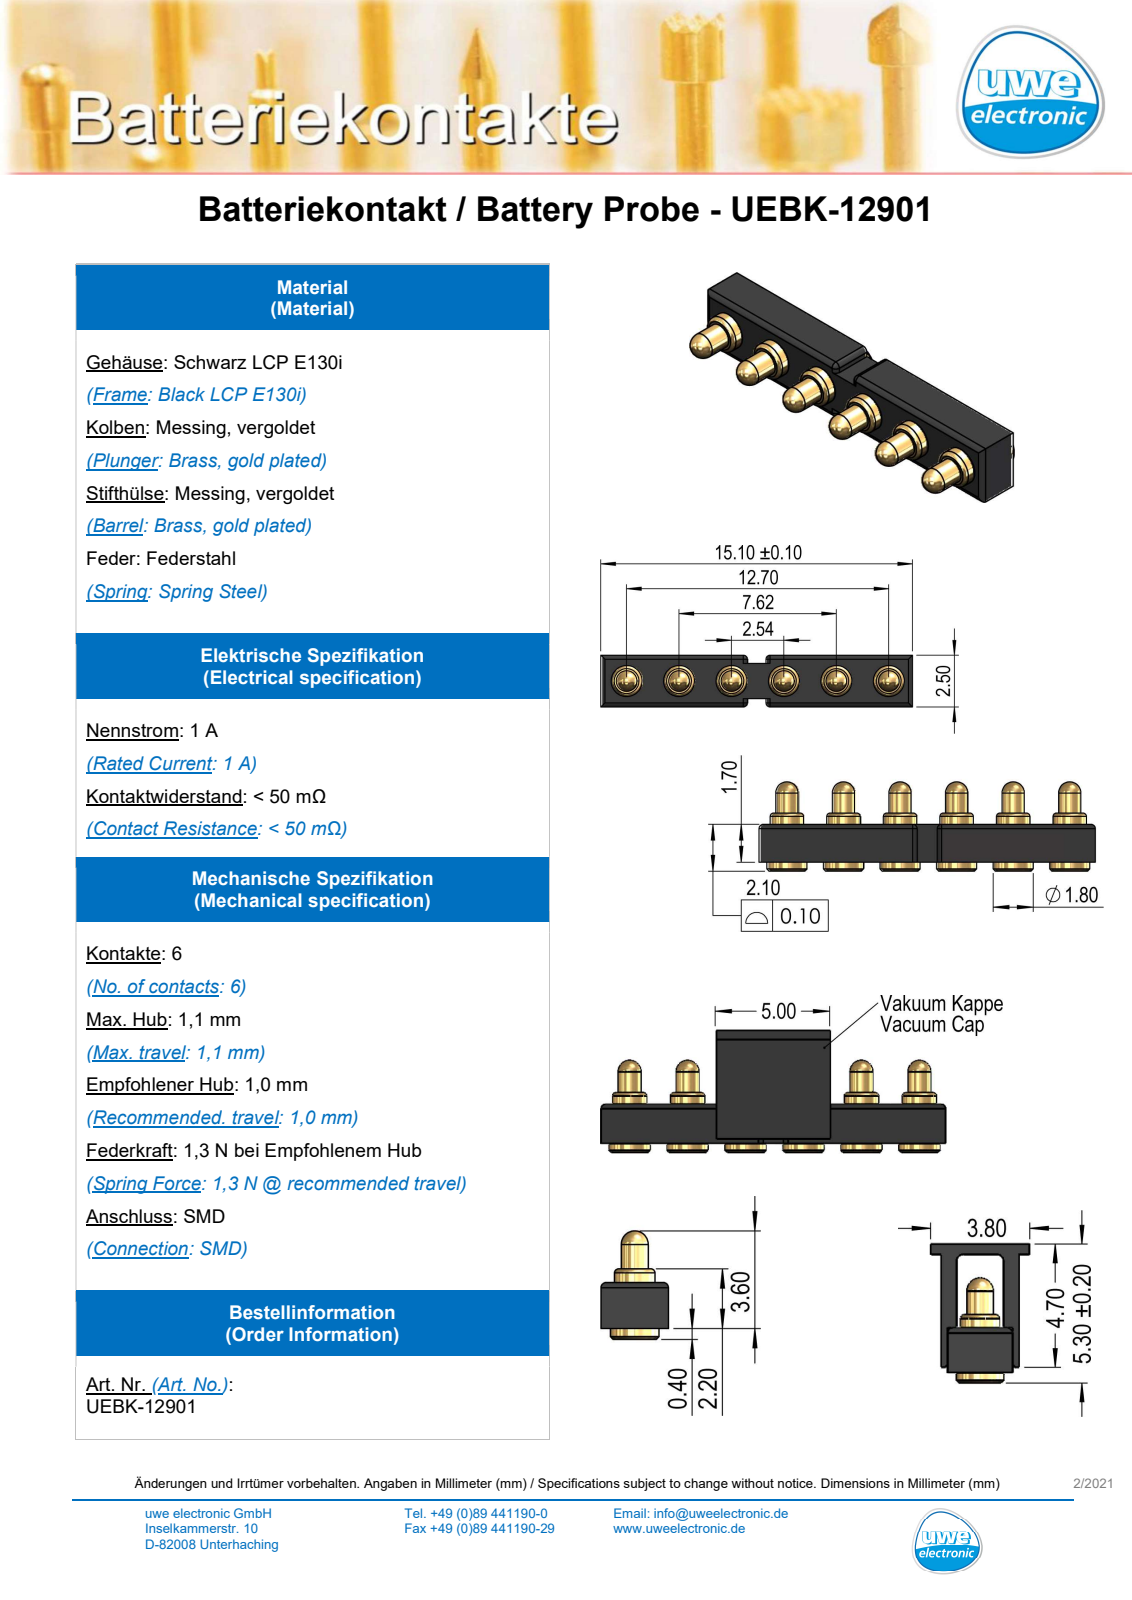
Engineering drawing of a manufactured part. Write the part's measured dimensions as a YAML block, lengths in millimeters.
part_name: "UEBK-12901-Pin; UEBK-12901; UEBK-12901-Gehäuse"
step_written_by: "SolidWorks 2020 (AUTOMOTIVE_DESIGN)"
units: millimeters
bodies: {solids: 7, faces: 134, planar: 32, cylindrical: 62, other: 40}
overall_size: [15.1, 4, 2.5]
volume: 80
surface_area: 284
round_holes:
  - {diameter: 1.5, count: 6}
round_bosses_or_shafts:
  - {diameter: 1.8, count: 6}
  - {diameter: 1, count: 6}
partial_cylinders:
  - {radius: 0.2, count: 10}
face_to_face_distances: [1.7, 2.5, 0.4, 2.1, 15.1, 2.6, 2.2, 0.5, 7.1, 8]
hole_center_spacings: [2.54, 5.08, 7.62, 10.16, 12.7]
